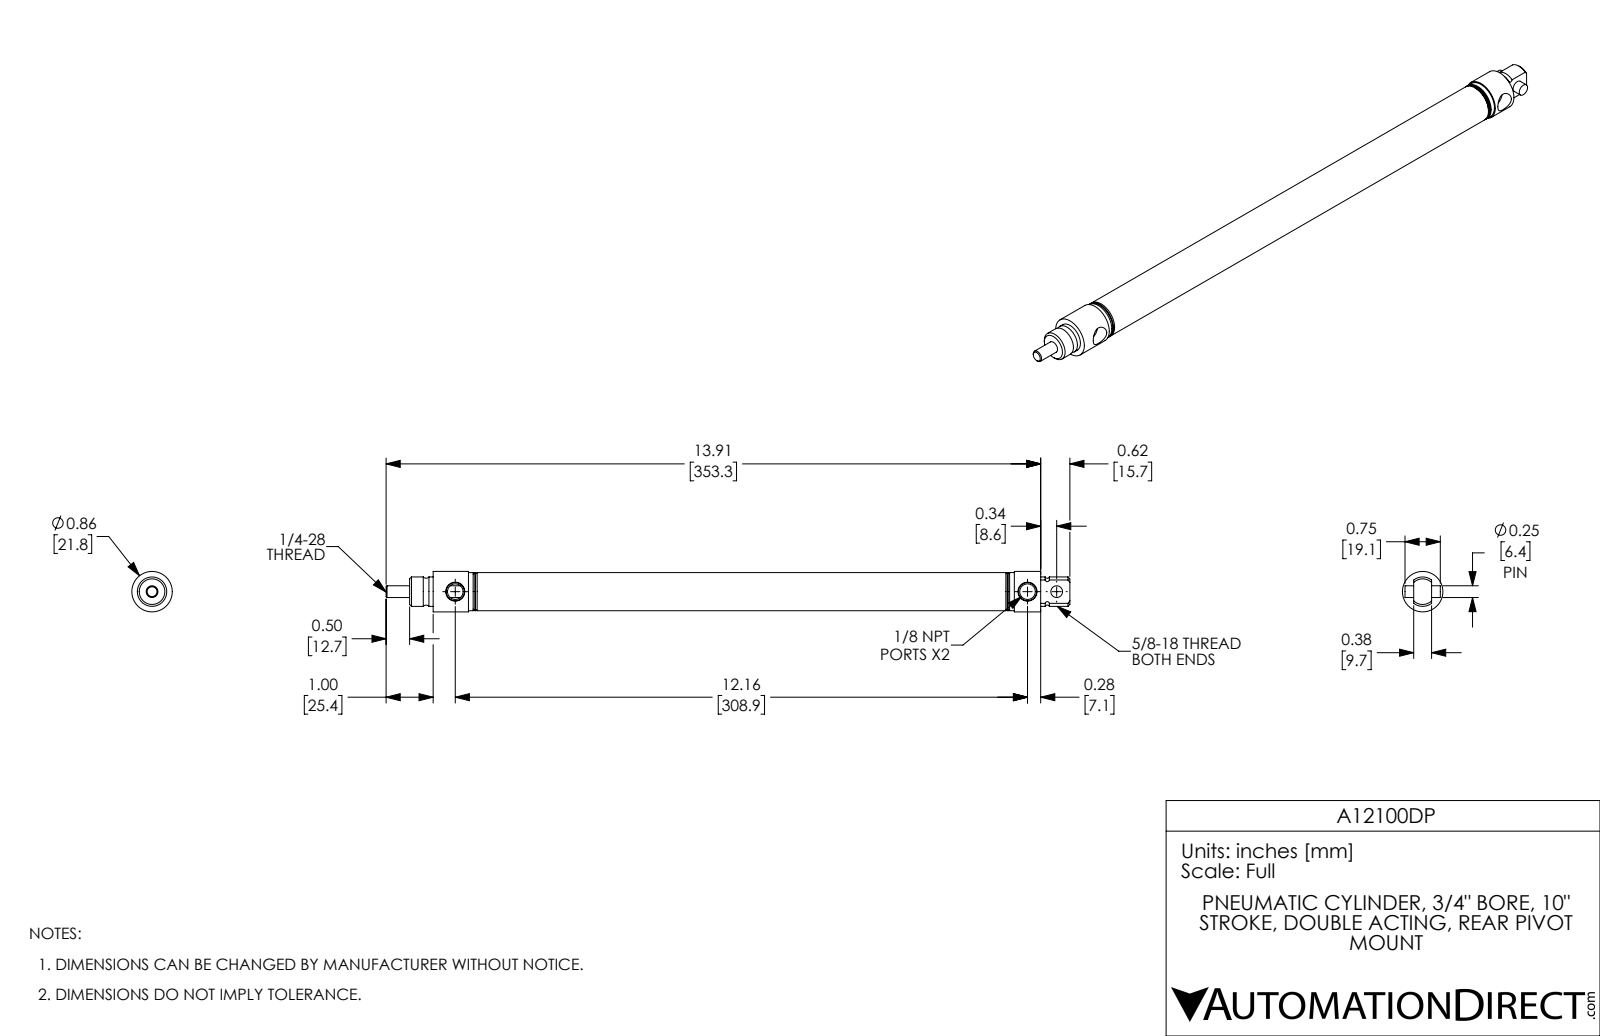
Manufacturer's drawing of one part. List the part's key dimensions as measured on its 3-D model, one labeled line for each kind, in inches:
Part name (STEP PRODUCT): A12100DP-PIN; A12100DP-Rod; A12100DP-MainBody; A12100DP
STEP written by: SolidWorks 2017 (AUTOMOTIVE_DESIGN)
Units: inches
Bodies: 3 solids, 91 faces (21 planar, 38 cylindrical, 32 other)
Overall size (bounding box): 14.53 × 0.86 × 0.86
Volume: 3.042 in³ · Surface area: 76.96 in²
Round holes (diameter × count): ⌀0.25 ×2, ⌀0.332 ×2, ⌀0.75 ×1
Round bosses / shafts (diameter × count): ⌀0.86 ×1, ⌀0.81 ×1, ⌀0.625 ×1
Main face-to-face distances: 0.5, 11.705, 10.5, 10, 1.205, 1.705, 11.705, 12.91, 11.205, 1.205
Hole centre spacings: 0.62, 12.16, 12.78
